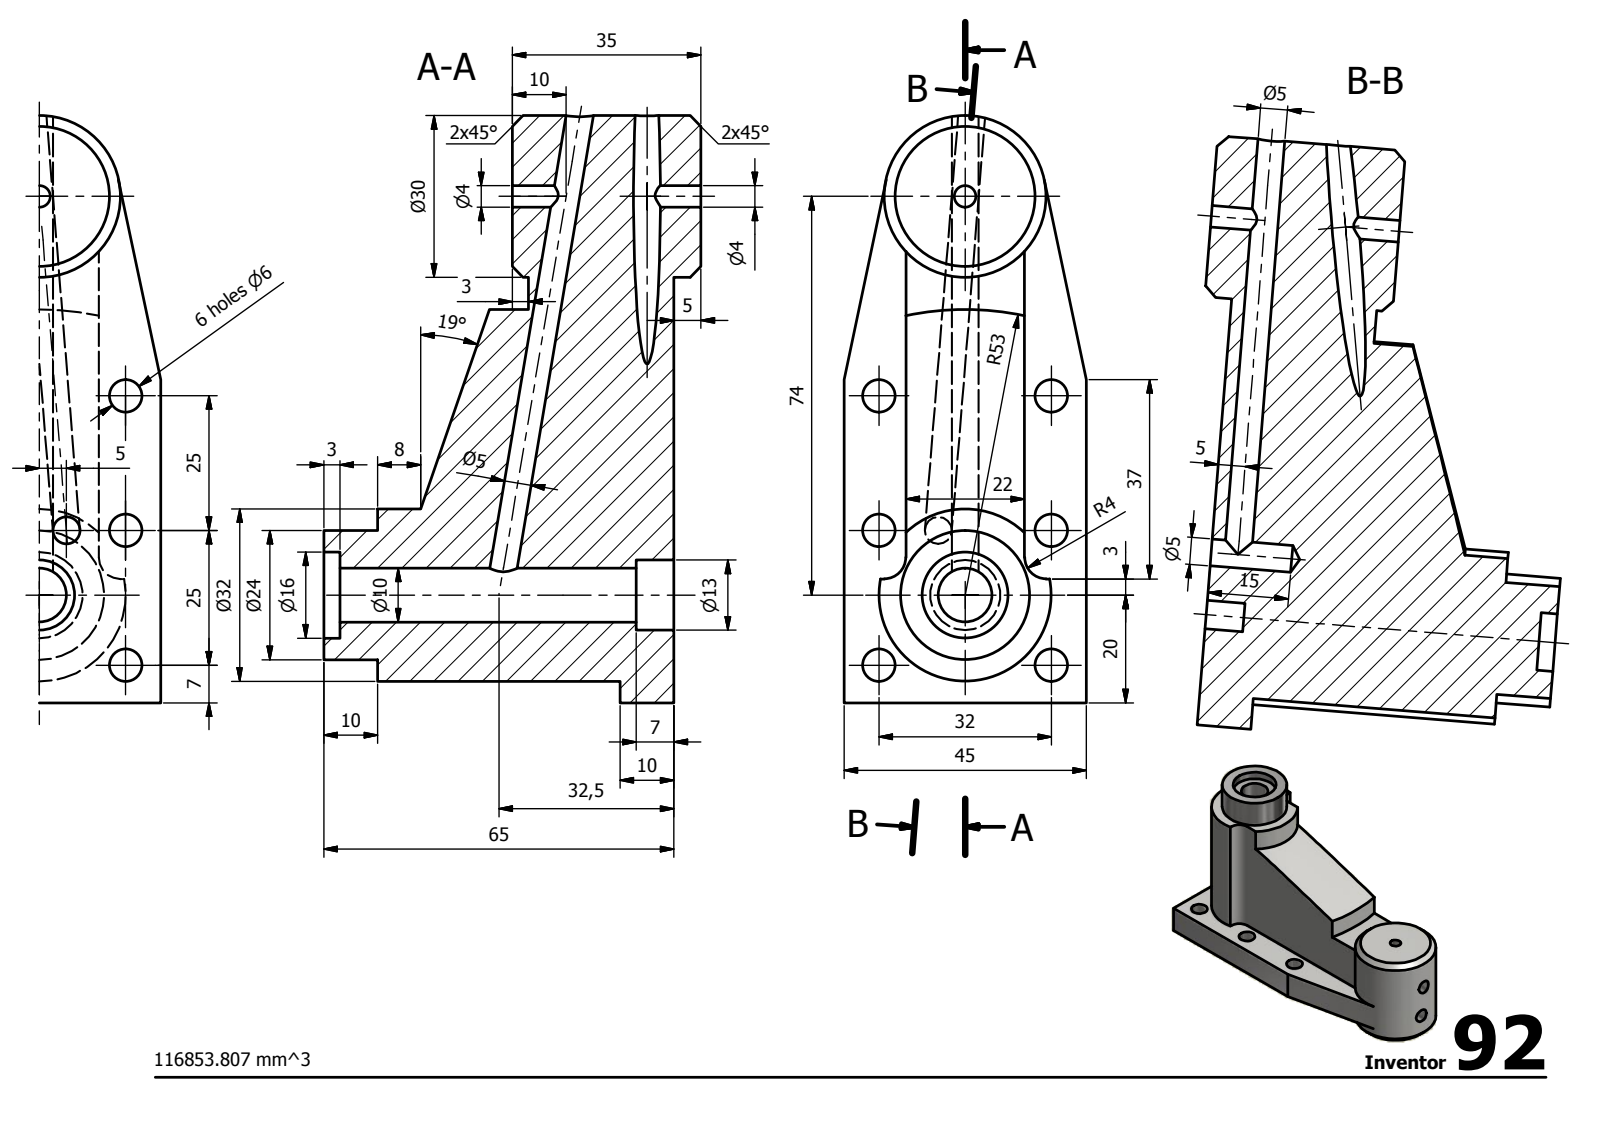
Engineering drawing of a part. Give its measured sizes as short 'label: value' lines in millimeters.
written by: Autodesk Inventor 2014 (AUTOMOTIVE_DESIGN)
unit: mm
bodies: 1 solid, 43 faces (18 planar, 21 cylindrical, 4 other)
size: 109 × 70 × 45
volume: 116 854 mm³; area: 26 455 mm²
holes: 6× ⌀6, 3× ⌀5, 1× ⌀4, 1× ⌀10, 1× ⌀13, 1× ⌀16
bosses: 1× ⌀32, 1× ⌀30, 1× ⌀24
rounds: 2× R4, 1× R53
face distances: 10, 22, 11.5, 33.5, 45, 35, 55, 20, 5, 15
hole spacings: 25, 40.31, 40.61, 32, 20, 20.62, 27.31, 32.65
